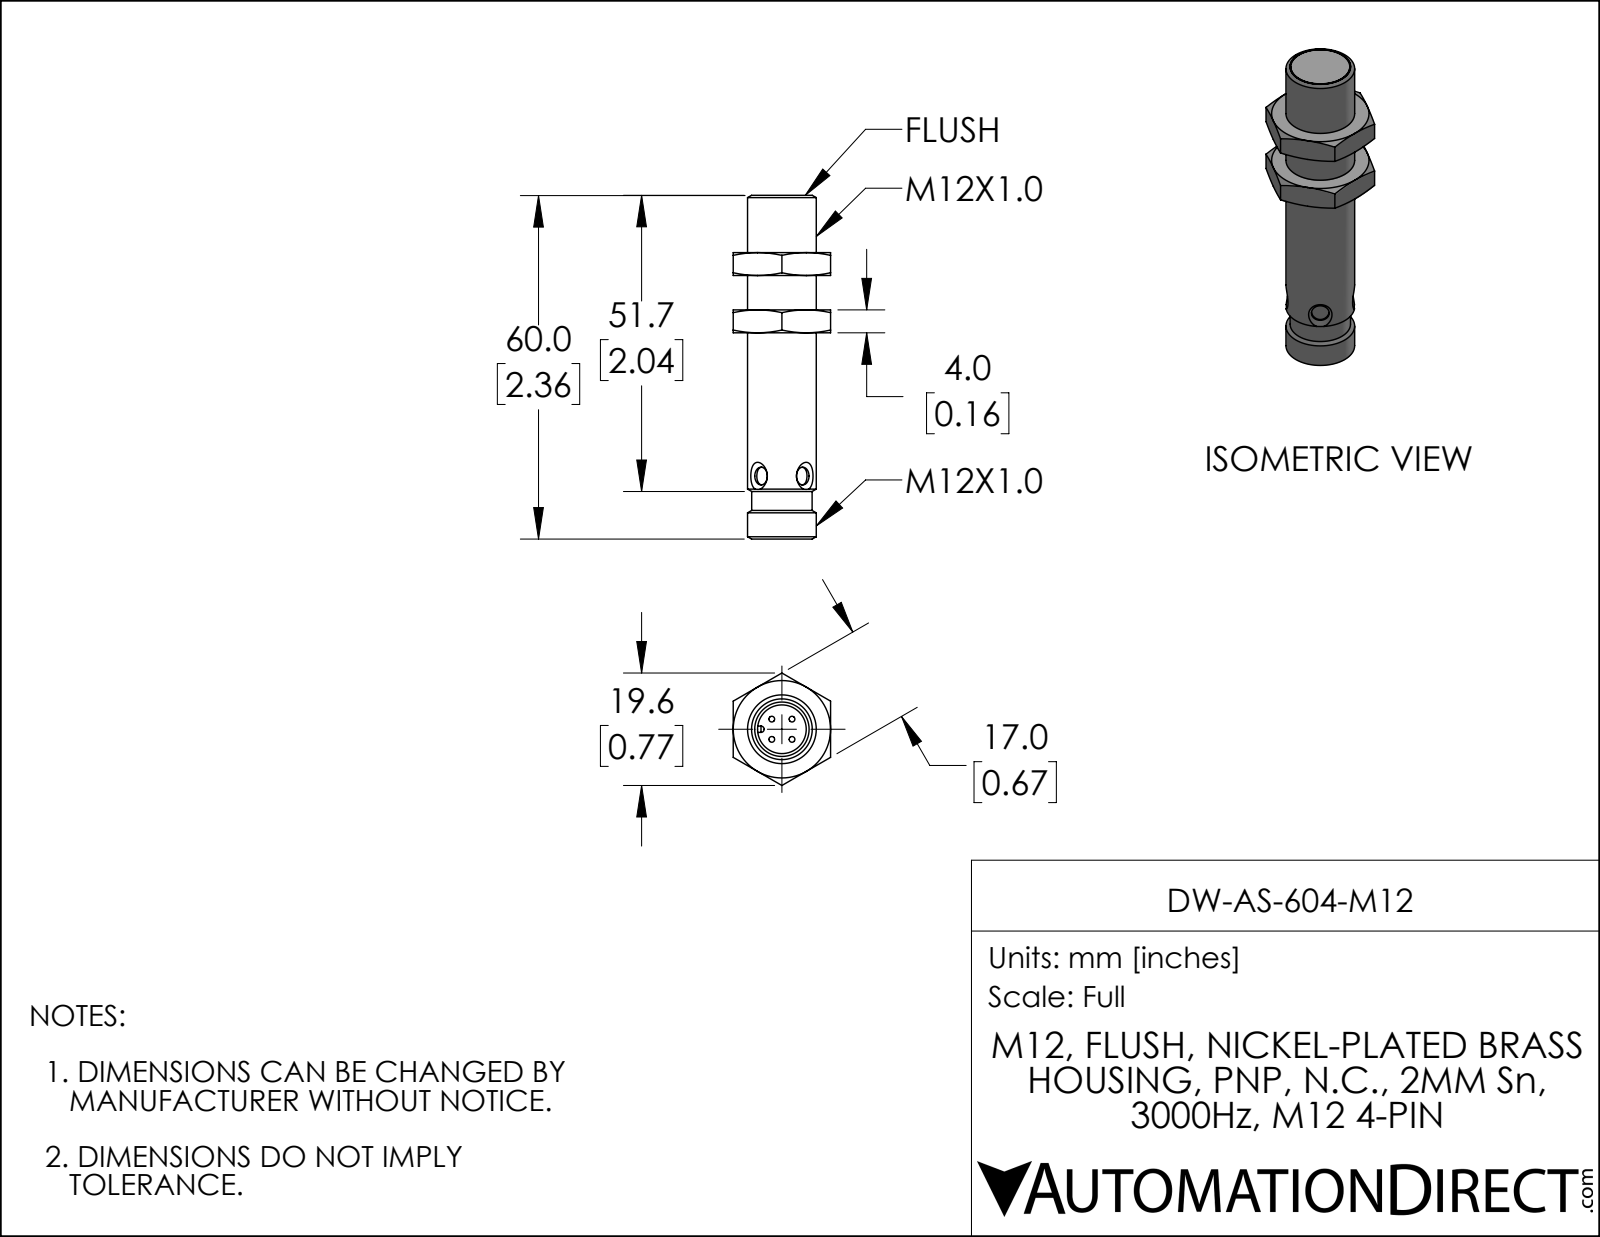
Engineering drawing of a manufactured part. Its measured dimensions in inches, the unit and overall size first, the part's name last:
Units: inches
Overall size (bounding box): 2.362 × 0.773 × 0.669
Round holes (diameter × count): ⌀0.122 ×2, ⌀0.335 ×1, ⌀0.415 ×1
Round bosses / shafts (diameter × count): ⌀0.039 ×4, ⌀0.472 ×1, ⌀0.415 ×1, ⌀0.406 ×1
Partial cylindrical surfaces — rounded edges, fillets, slot ends (radius × count): R0.022 ×2, R0.193 ×1
Main face-to-face distances: 0.394, 0.157, 0.669, 0.551, 0.236, 0.787, 0.945, 2.02, 1.626, 1.469
Volume: 0.443 in³ · Surface area: 5.454 in²
Bodies: 1 solid, 83 faces (23 planar, 22 cylindrical, 38 other)
Part name (STEP PRODUCT): DW-AS-604-M12
STEP written by: SolidWorks 2019 (AUTOMOTIVE_DESIGN)
